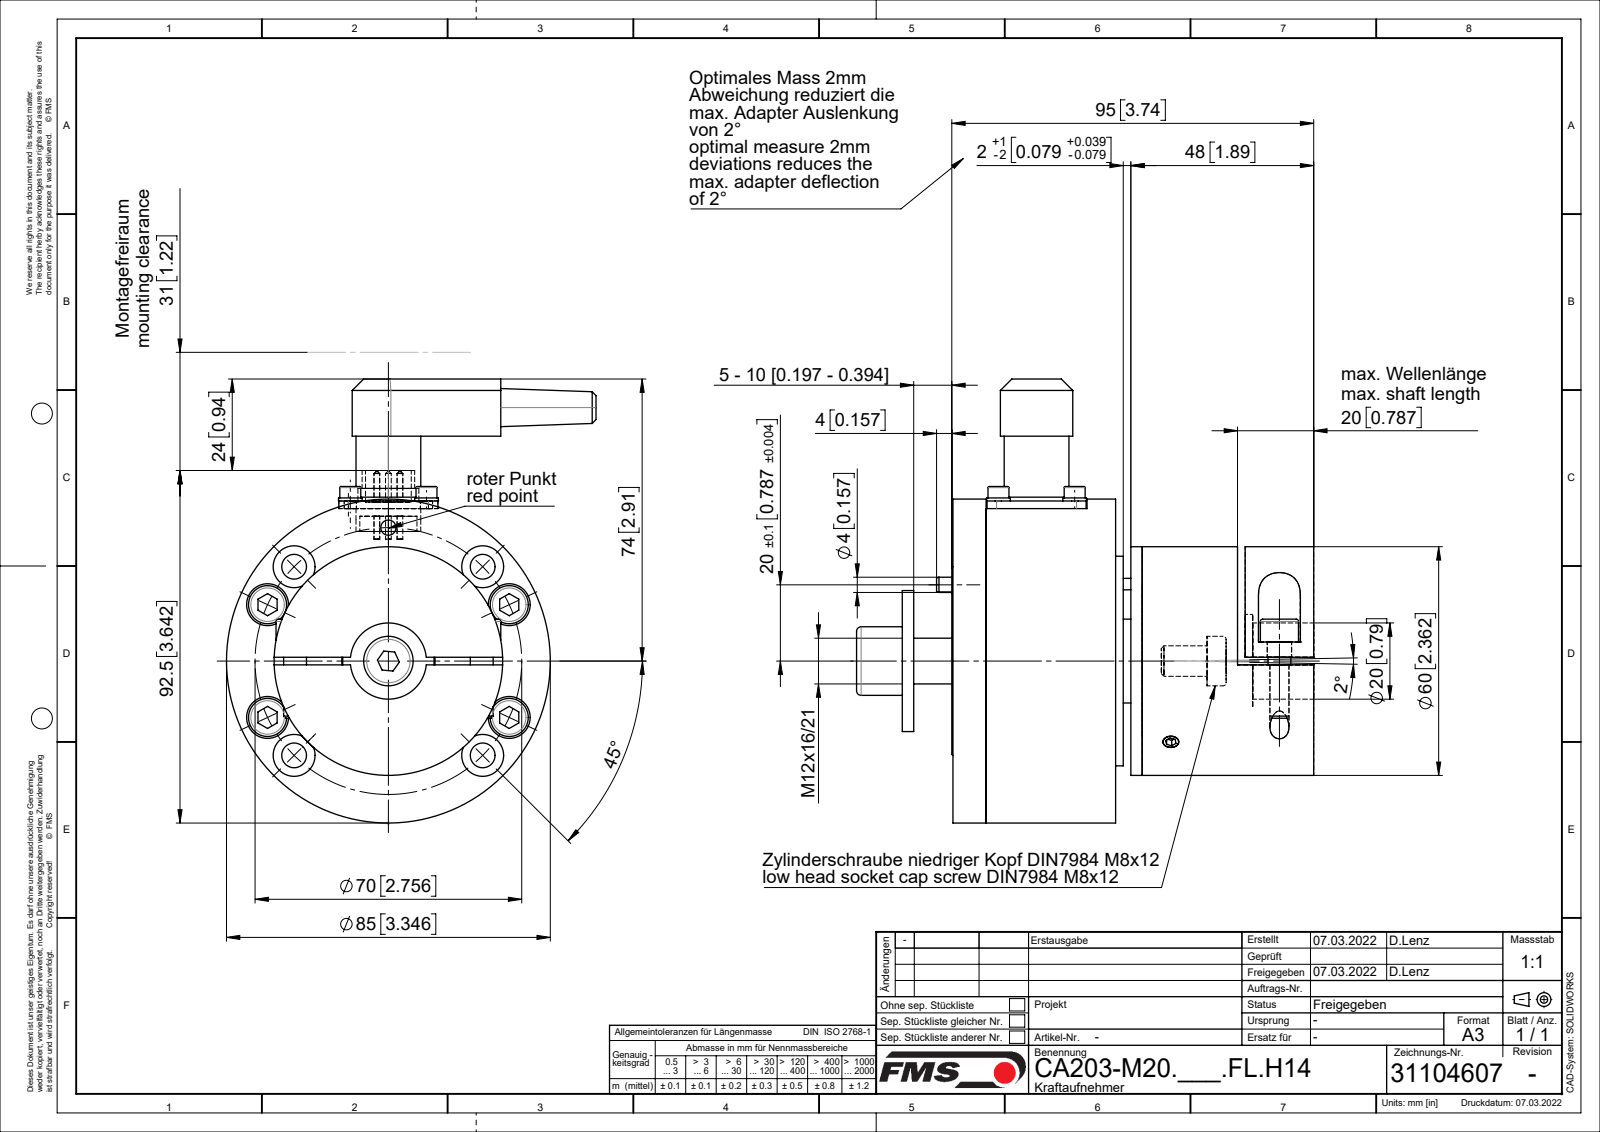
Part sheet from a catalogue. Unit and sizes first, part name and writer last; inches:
Units: inches
Overall size (bounding box): 4.724 × 4.587 × 3.819
Round holes (diameter × count): ⌀0.098 ×8, ⌀0.256 ×8, ⌀0.433 ×8, ⌀0.197 ×6, ⌀0.079 ×5, ⌀0.157 ×5, ⌀0.122 ×4, ⌀0.126 ×4, ⌀0.142 ×4, ⌀0.276 ×4, ⌀0.118 ×2, ⌀0.252 ×2
Round bosses / shafts (diameter × count): ⌀0.118 ×8, ⌀0.236 ×7, ⌀0.394 ×6, ⌀0.059 ×5, ⌀0.244 ×4, ⌀0.224 ×4, ⌀0.217 ×4, ⌀3.346 ×1
Partial cylindrical surfaces — rounded edges, fillets, slot ends (radius × count): R0.098 ×4, R0.197 ×2, R0.217 ×2, R0.374 ×1
Main face-to-face distances: 0.079, 1.772, 1.614, 0.394, 1.181, 0.118, 2.362, 1.339, 1.969, 0.866
Hole centre spacings: 1.378, 0.787, 0.976, 0.992, 1.291, 2.013, 2.223, 0.236
Volume: 19.41 in³ · Surface area: 176.8 in²
Bodies: 43 solids, 810 faces (280 planar, 338 cylindrical, 192 other)
Part name (STEP PRODUCT): 070908-1_stp_01; Zyl-Schr DIN912_M12x25; 31104607; 070907-2_01 (+8 more)
STEP written by: SolidWorks 2018 (CONFIG_CONTROL_DESIGN)
